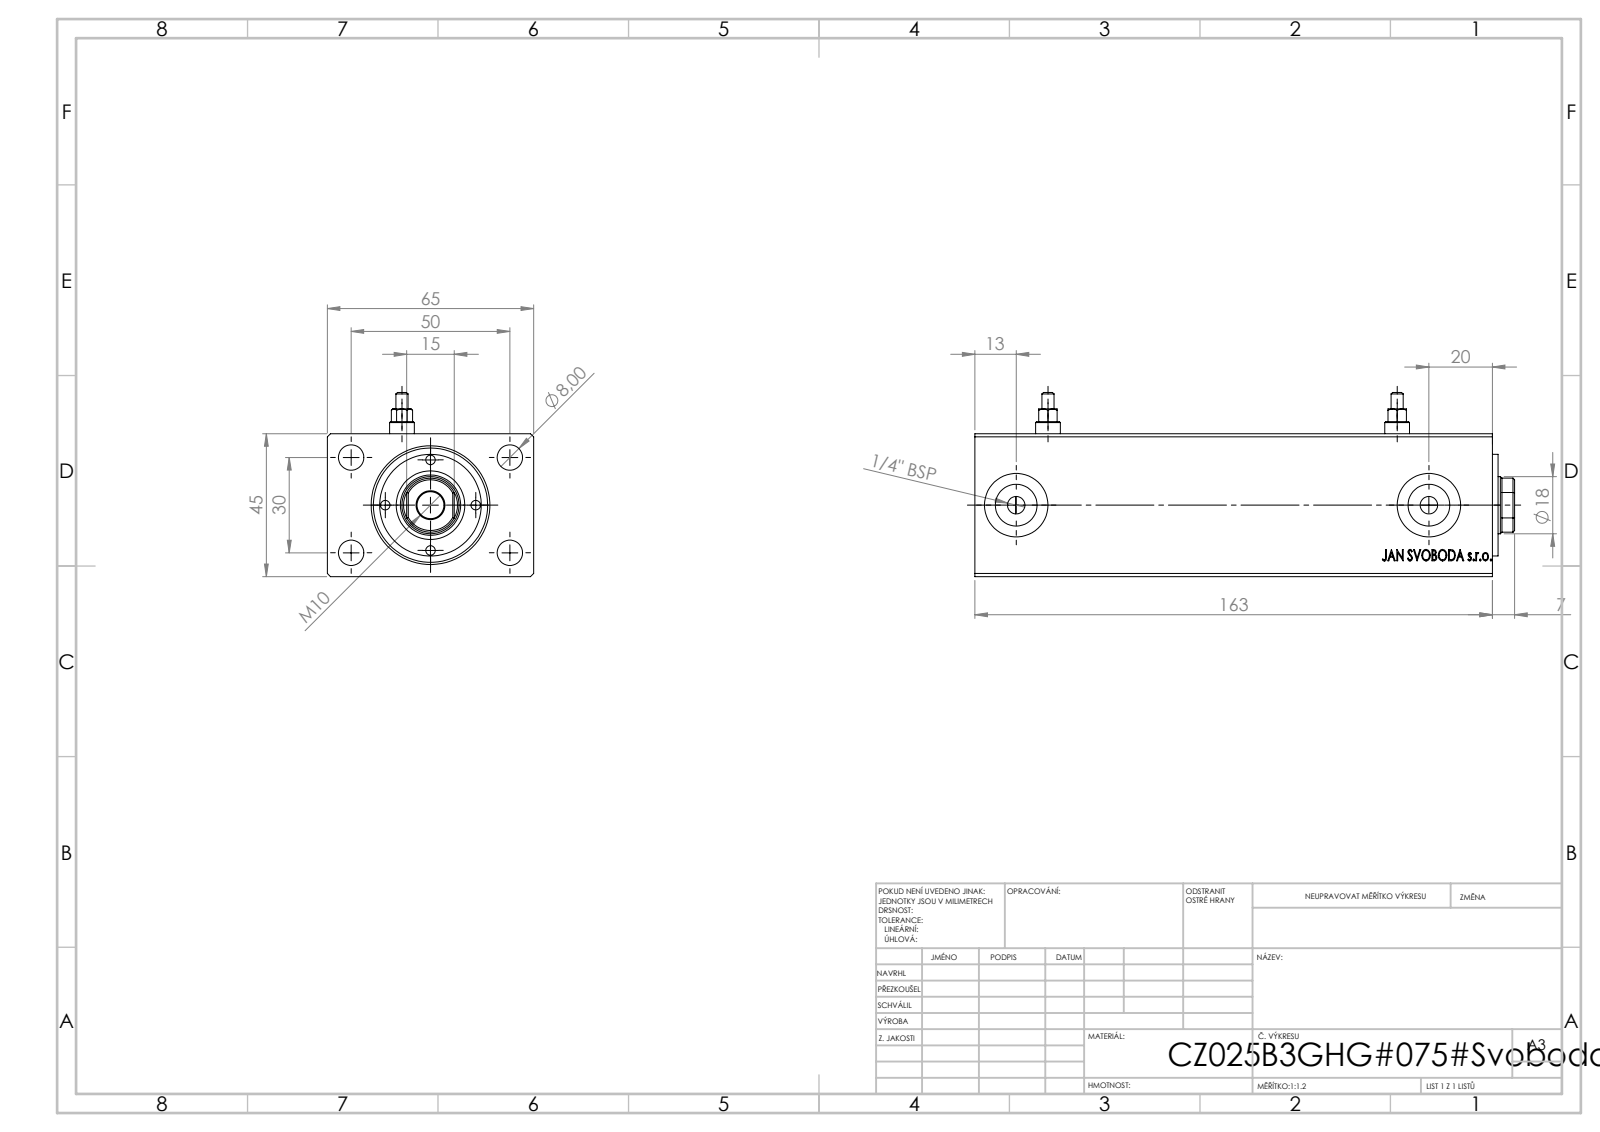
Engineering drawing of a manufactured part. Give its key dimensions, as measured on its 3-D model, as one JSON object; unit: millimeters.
{"part_name": "V500CZ_B_VC; V500CZ; Zatka_Cushioning3", "step_written_by": "SolidWorks 2019 (CONFIG_CONTROL_DESIGN)", "units": "millimeters", "bodies": {"solids": 5, "faces": 933, "planar": 423, "cylindrical": 74, "other": 436}, "overall_size": [170, 65, 58], "volume_mm3": 445121, "surface_area_mm2": 74950, "round_holes": [[8, 6], [3, 4], [1.8, 2], [5.5, 2], [13.16, 2], [20, 2], [8.5, 1], [18, 1], [19, 1], [25, 1], [36, 1]], "round_bosses_or_shafts": [[7.8, 2], [3.8, 2], [32, 1]], "partial_cylinders_radius": [[8.5, 1]], "face_to_face_distances": [45, 65, 163, 7, 162.8, 12.8, 150.2, 12.6, 1.8, 5.2], "hole_center_spacings": [14.25, 18.45, 20.15, 25.01, 29.15, 38.48, 42.02, 28.5]}
